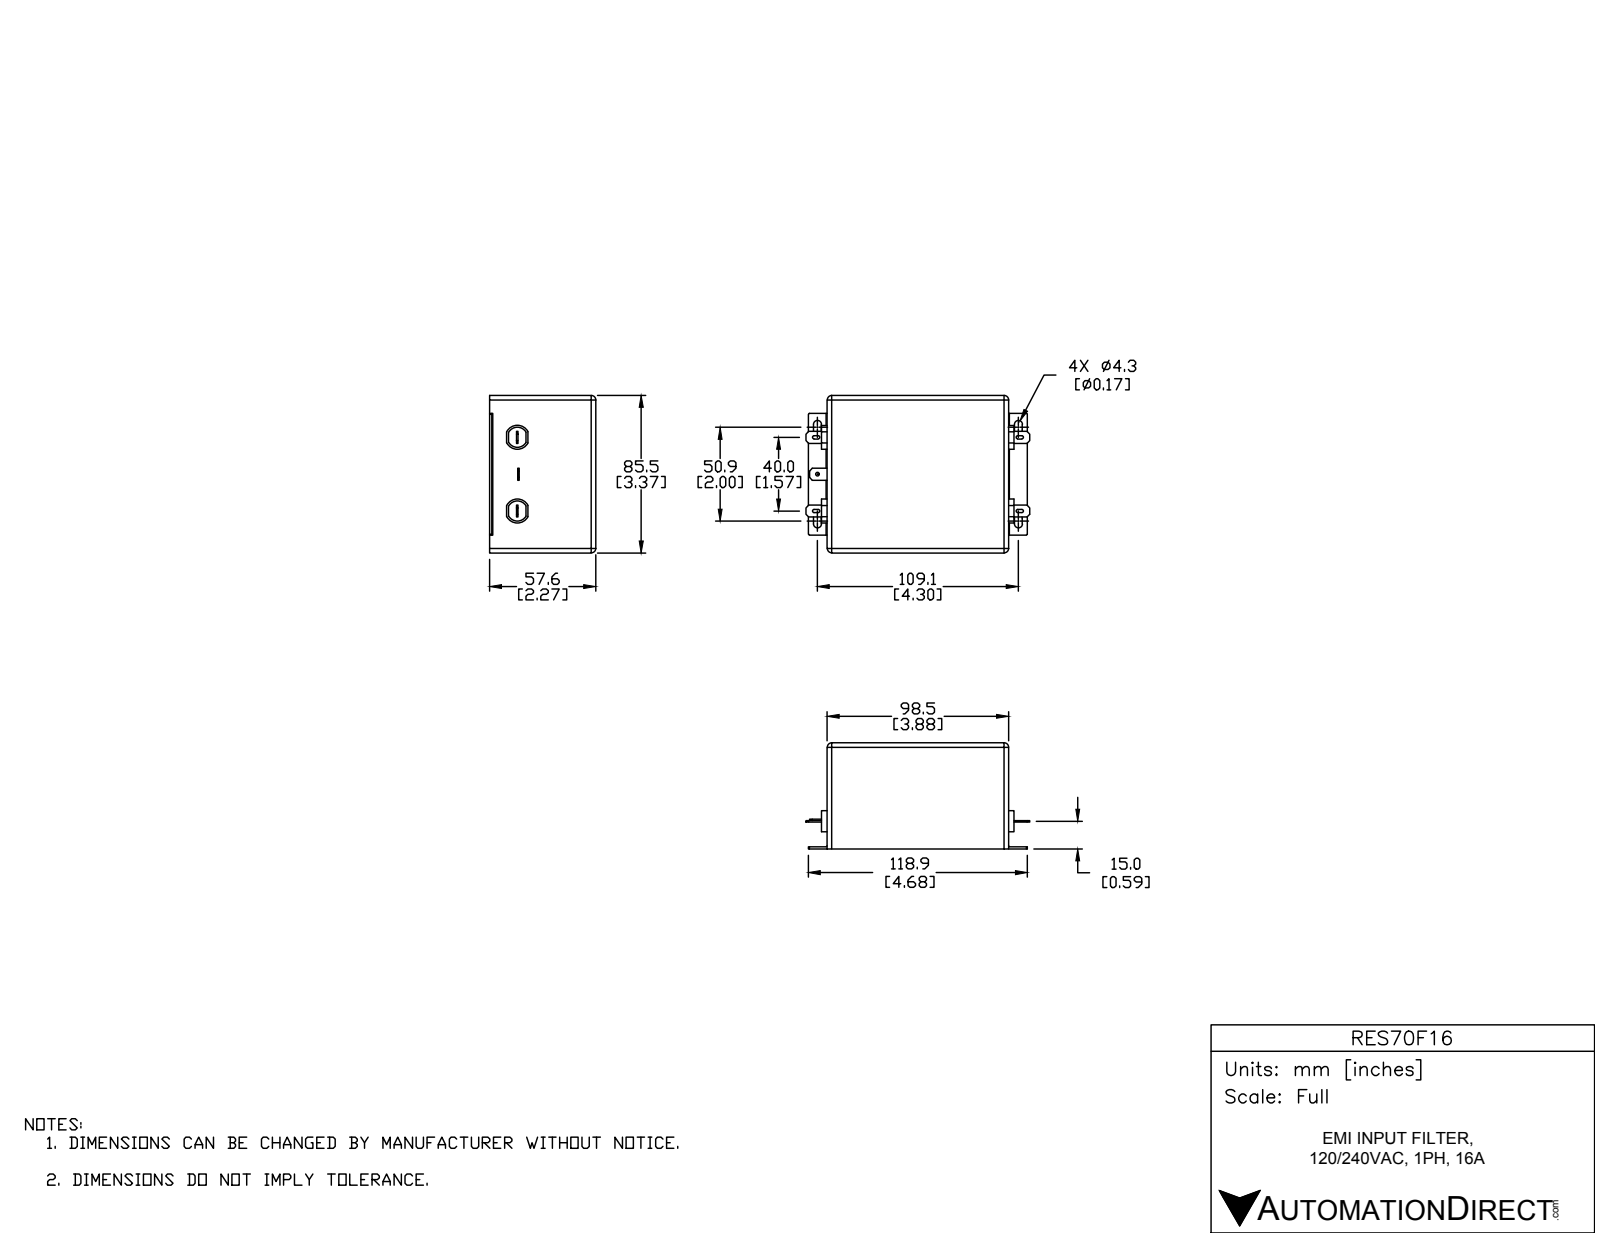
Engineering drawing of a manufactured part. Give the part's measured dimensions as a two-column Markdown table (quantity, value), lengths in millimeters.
| quantity | value |
| --- | --- |
| part name | RES70F16 |
| STEP written by | SolidWorks 2015 (AUTOMOTIVE_DESIGN) |
| units | millimeters |
| bodies | 1 solid, 153 faces (89 planar, 60 cylindrical, 4 other) |
| overall size | 121.5 × 85.5 × 57.6 |
| volume | 486 998 mm³ |
| surface area | 41 335 mm² |
| round holes (diameter × count) | 2 × 1 |
| partial cylindrical surfaces (radius × count) | 0.88 × 8, 2.15 × 8, 2.5 × 8, 0.5 × 6, 5.5 × 2, 6.5 × 2 |
| main face-to-face distances | 57.6, 85.5, 98.5, 1.2, 56.4, 1.5, 100, 101.5, 0.8, 15.4 |
